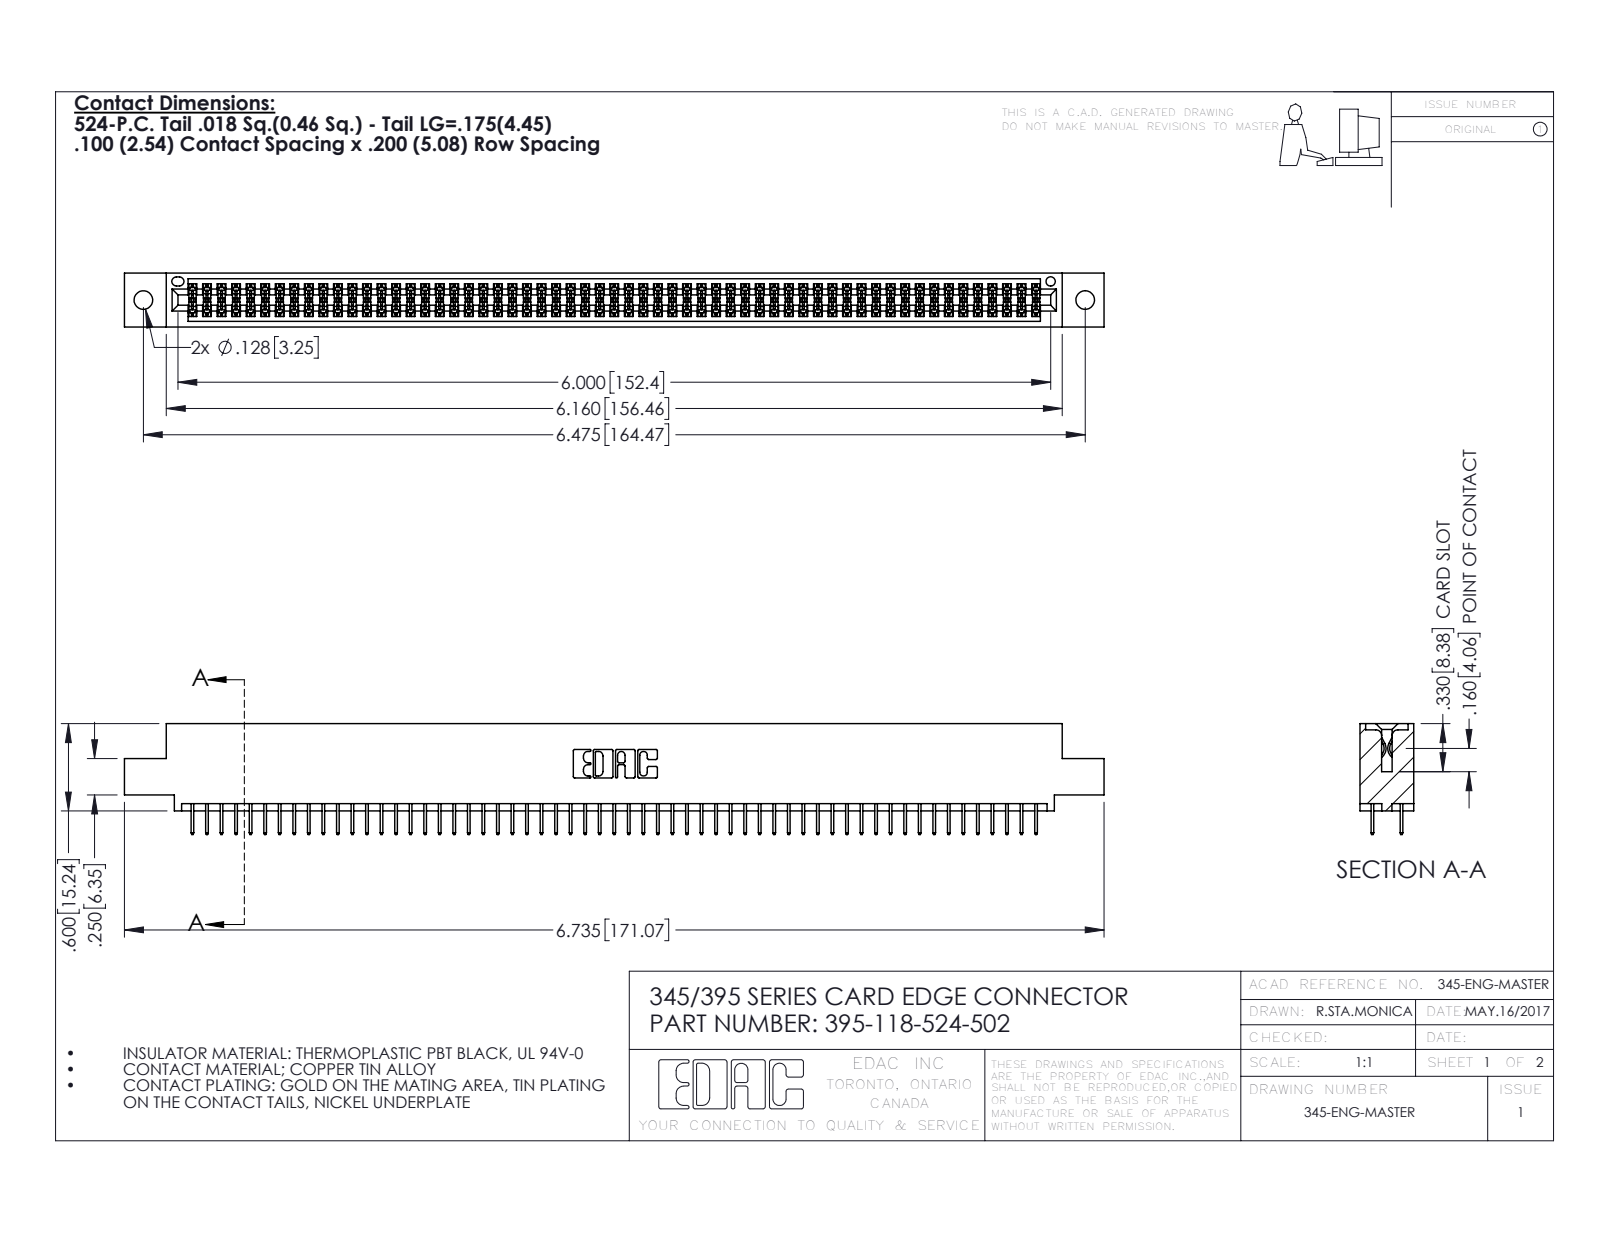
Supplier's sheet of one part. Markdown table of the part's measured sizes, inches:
| quantity | value |
| --- | --- |
| part name | 395-118-524-502; 345 Part_0.110 Offset - 0.128 Dia; 345-292-001_345-293-124 |
| STEP written by | SolidWorks 2016 (CONFIG_CONTROL_DESIGN) |
| units | inches |
| bodies | 119 solids, 6502 faces (4686 planar, 1816 cylindrical, 0 other) |
| overall size | 6.735 × 0.762 × 0.37 |
| volume | 1.006 in³ |
| surface area | 37.28 in² |
| round holes (diameter × count) | 0.128 × 2, 0.064 × 1 |
| partial cylindrical surfaces (radius × count) | 0.006 × 177, 0.01 × 22, 0.007 × 6, 0.031 × 6, 0.026 × 3, 0.014 × 2, 0.019 × 2, 0.022 × 2 |
| main face-to-face distances | 0.072, 0.298, 0.2, 0.37, 0.098, 0.272, 0.025, 0.225, 0.072, 0.175 |
| hole center spacings | 0.27, 6.239, 6.475 |
